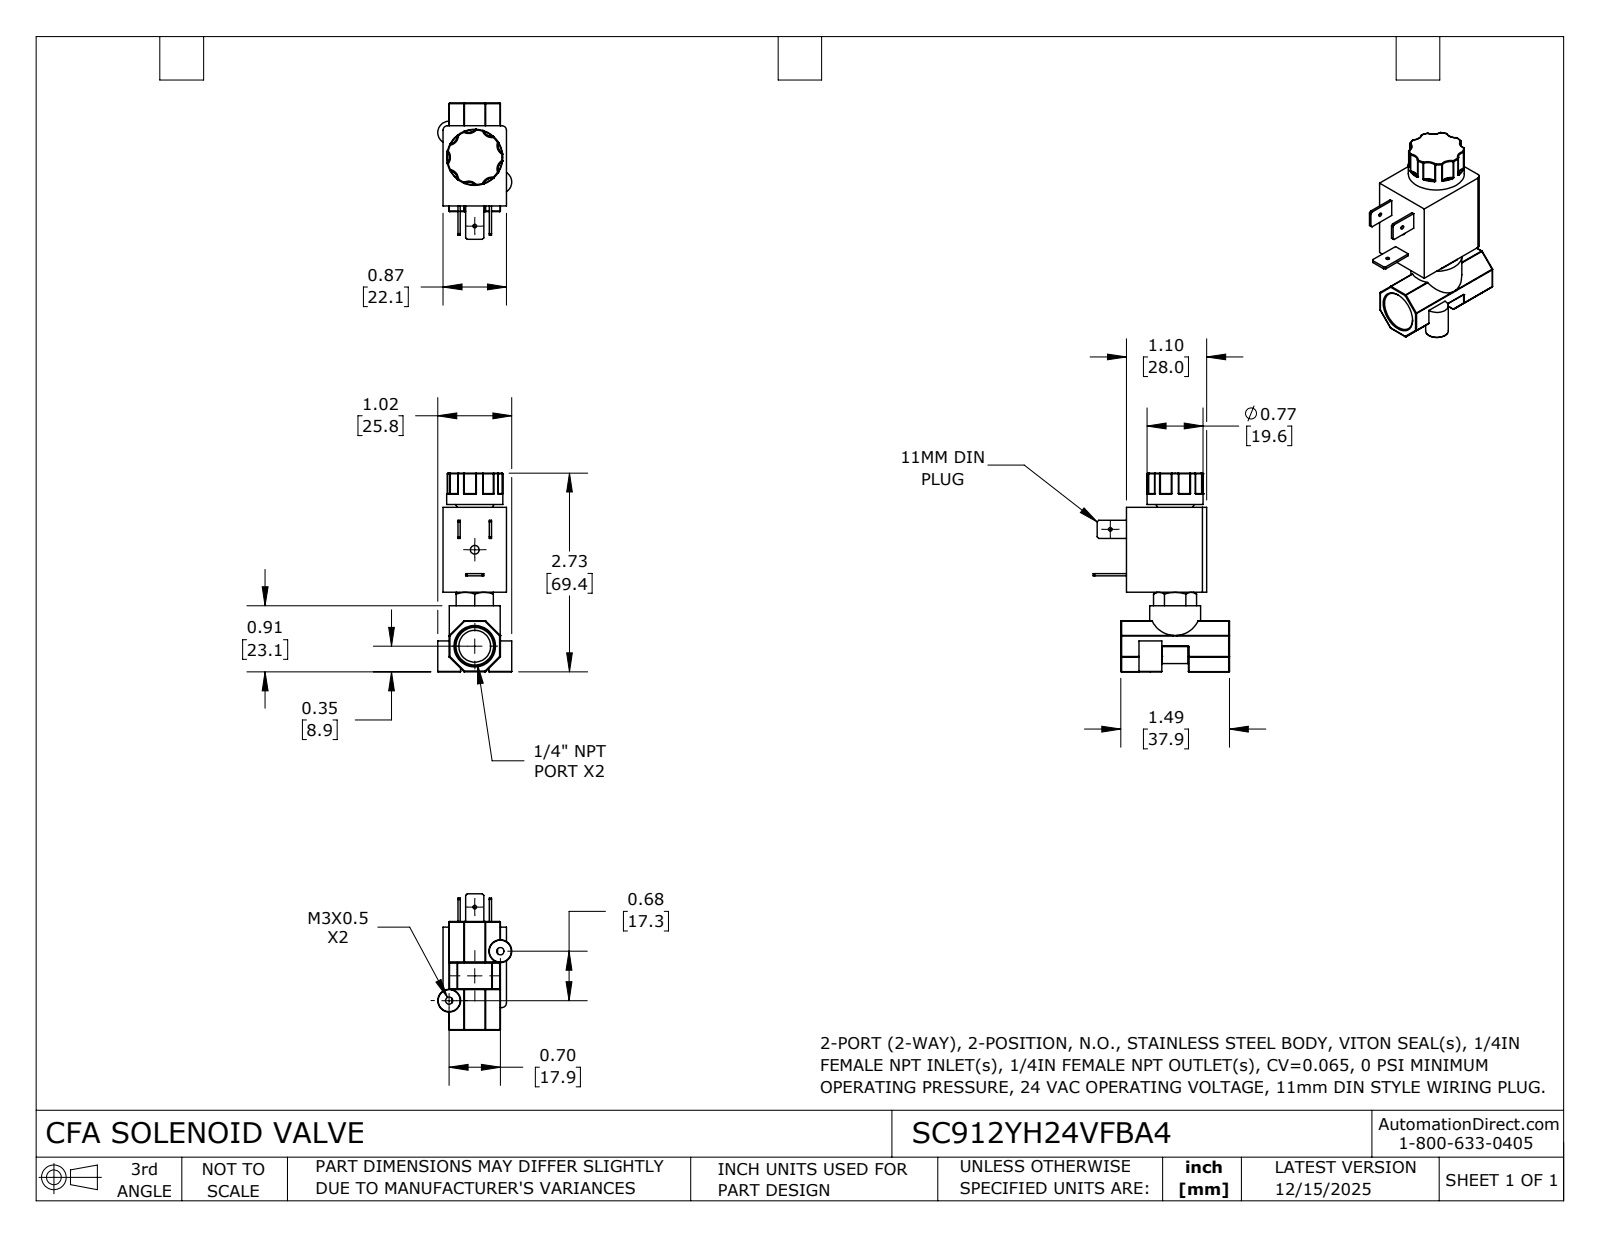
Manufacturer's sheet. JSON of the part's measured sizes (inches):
{"part_name": "SC912YH24VFBA4", "step_written_by": "SolidWorks 2024 (CONFIG_CONTROL_DESIGN)", "units": "inches", "bodies": {"solids": 1, "faces": 350, "planar": 74, "cylindrical": 107, "other": 169}, "overall_size": [2.731, 1.874, 1.017], "volume_in3": 1.823, "surface_area_in2": 16.29, "round_holes": [[0.05, 2], [0.1, 2], [0.12, 1], [0.438, 1]], "round_bosses_or_shafts": [[0.313, 2], [0.77, 1], [0.7, 1]], "partial_cylinders_radius": [[0.01, 42], [0.005, 14], [0.133, 7], [0.06, 2], [0.132, 2], [0.237, 1], [0.314, 1]], "face_to_face_distances": [0.87, 0.704, 1.104, 1.167, 0.083, 0.787, 1.094, 2.261, 2.731, 1.637], "hole_center_spacings": [0.7, 0.979, 1.326, 1.333]}
